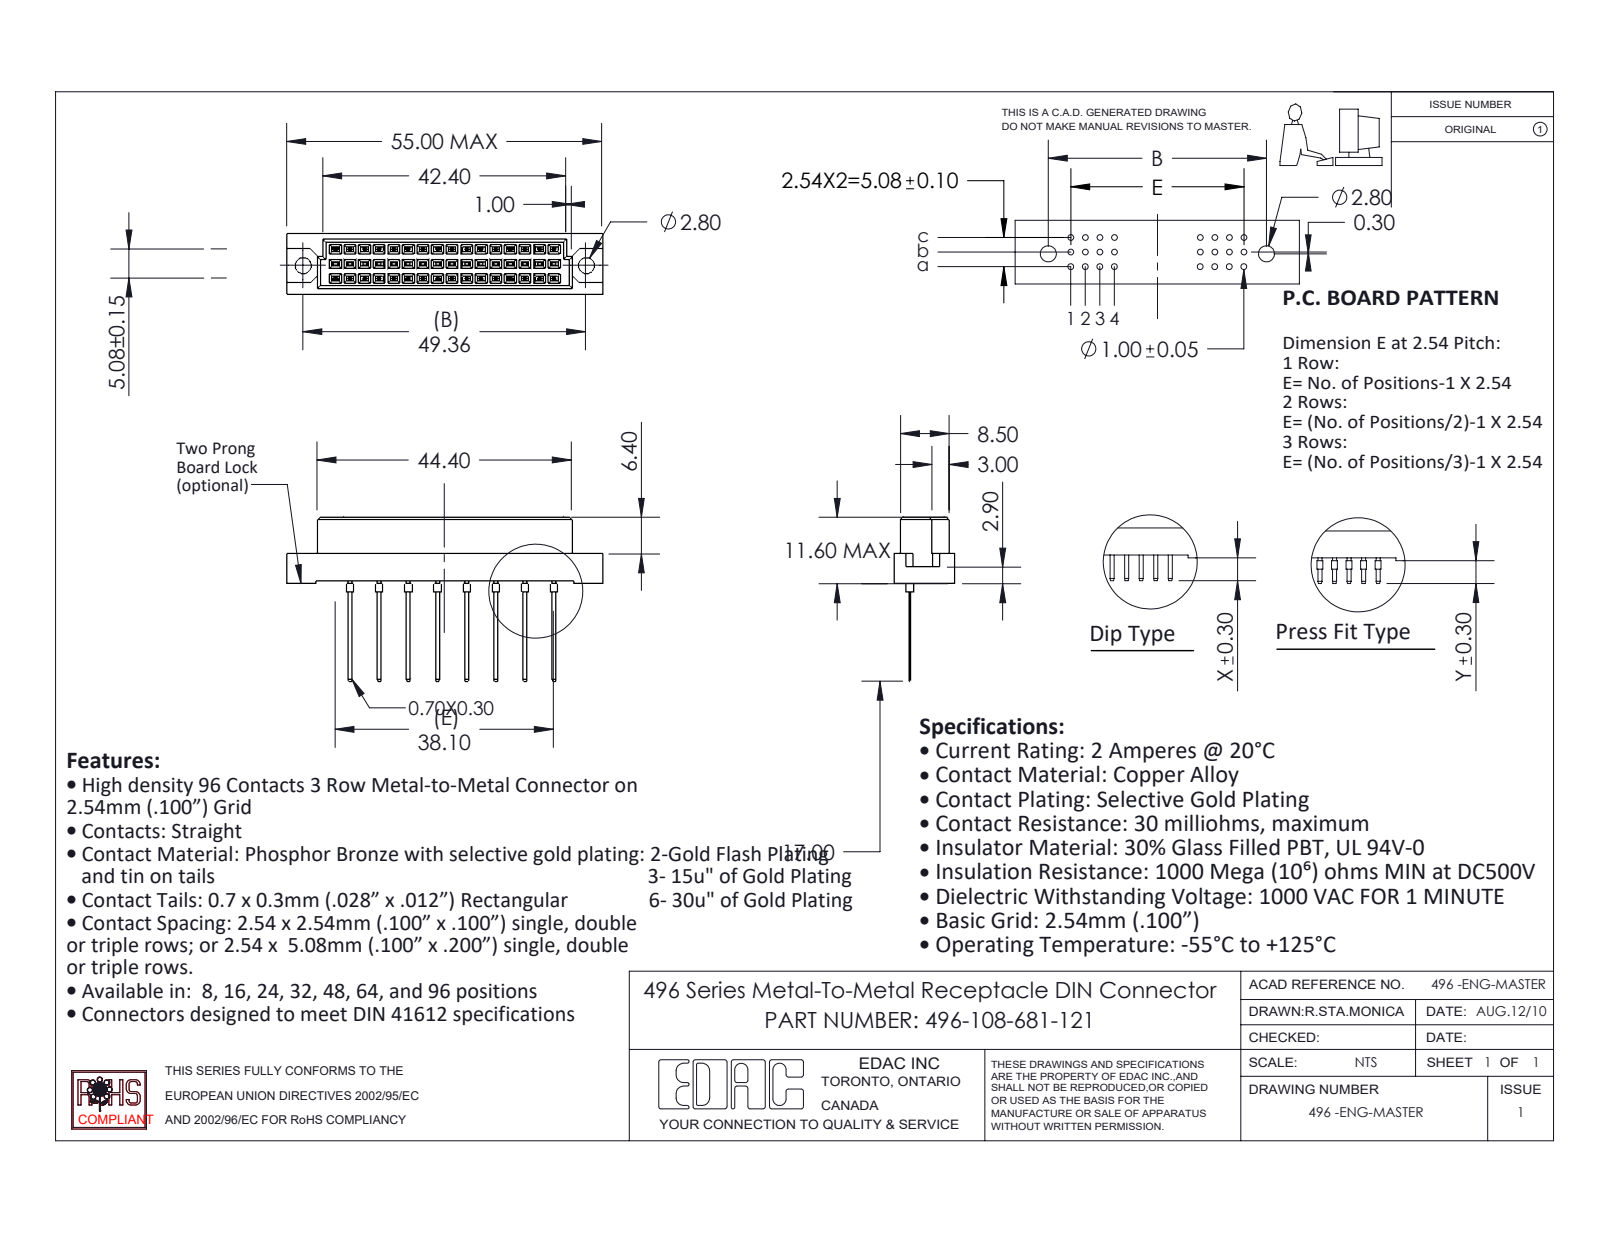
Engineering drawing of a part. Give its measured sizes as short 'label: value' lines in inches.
name: 496-108-681-121; 496 Part_48; 496-290_81
written by: SolidWorks 2020 (CONFIG_CONTROL_DESIGN)
unit: in
bodies: 9 solids, 810 faces (790 planar, 20 cylindrical, 0 other)
size: 2.165 × 1.126 × 0.417
volume: 0.283 in³; area: 7.111 in²
holes: 2× ⌀0.11
bosses: 8× ⌀0.039
face distances: 0.1, 0.2, 0.041, 0.376, 0.032, 0.417, 0.132, 0.068, 0.335, 0.022
hole spacings: 1.943
